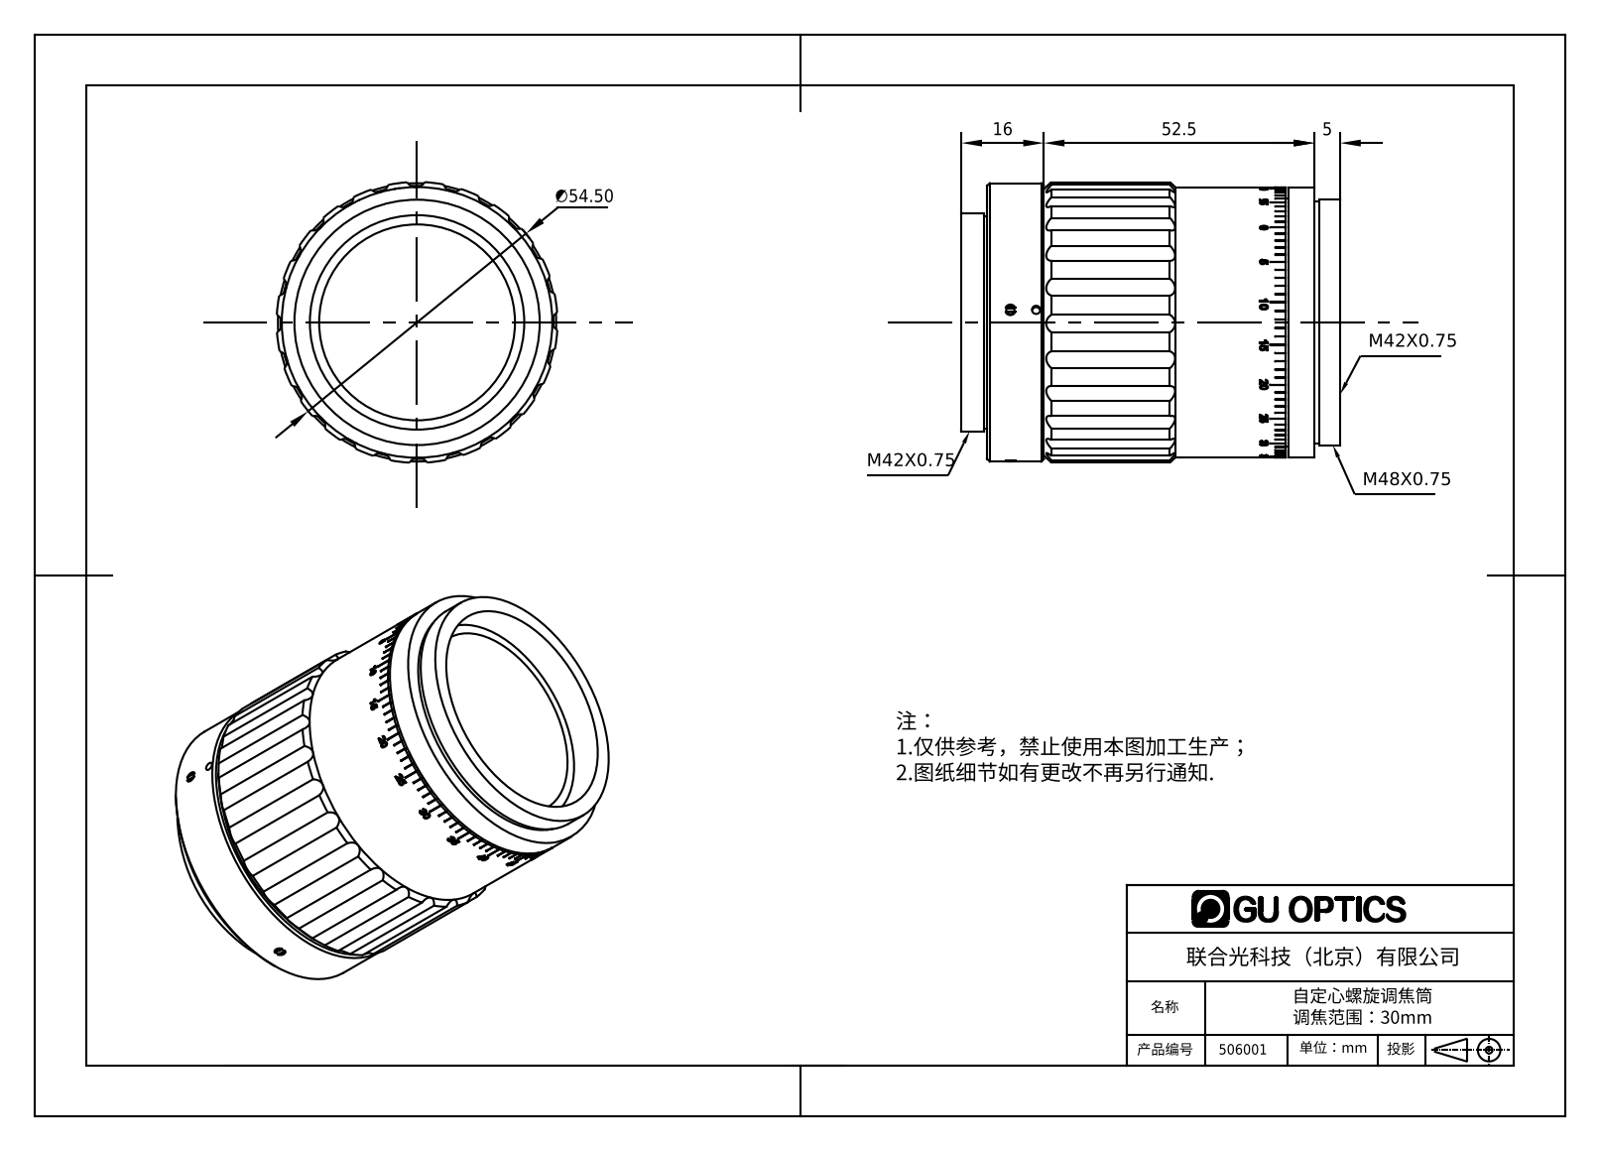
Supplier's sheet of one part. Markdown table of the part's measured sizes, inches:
| quantity | value |
| --- | --- |
| part name | 506000调教手轮; M42锁紧环; 506000定位筒; 506000自定心连动圈 (+2 more) |
| STEP written by | SolidWorks 2016 (AUTOMOTIVE_DESIGN) |
| units | inches |
| bodies | 8 solids, 1069 faces (347 planar, 380 cylindrical, 342 other) |
| overall size | 2.894 × 2.143 × 2.143 |
| volume | 4.133 in³ |
| surface area | 94.51 in² |
| round holes (diameter × count) | 0.063 × 5, 0.083 × 3, 1.496 × 1, 1.638 × 1, 1.732 × 1, 1.752 × 1, 1.76 × 1, 1.878 × 1, 1.949 × 1, 2.008 × 1 |
| round bosses / shafts (diameter × count) | 0.081 × 4, 0.079 × 4, 2.126 × 1, 2.067 × 1, 1.992 × 1, 1.89 × 1, 1.874 × 1, 1.87 × 1 |
| partial cylindrical surfaces (radius × count) | 0.079 × 24, 0.876 × 4, 0.866 × 3, 1.033 × 1, 1.073 × 1 |
| main face-to-face distances | 0.472, 0.079, 0.197, 0.394, 0.551, 0.039, 2.224, 2.5, 2.697, 2.029 |
| hole center spacings | 0.197 |
